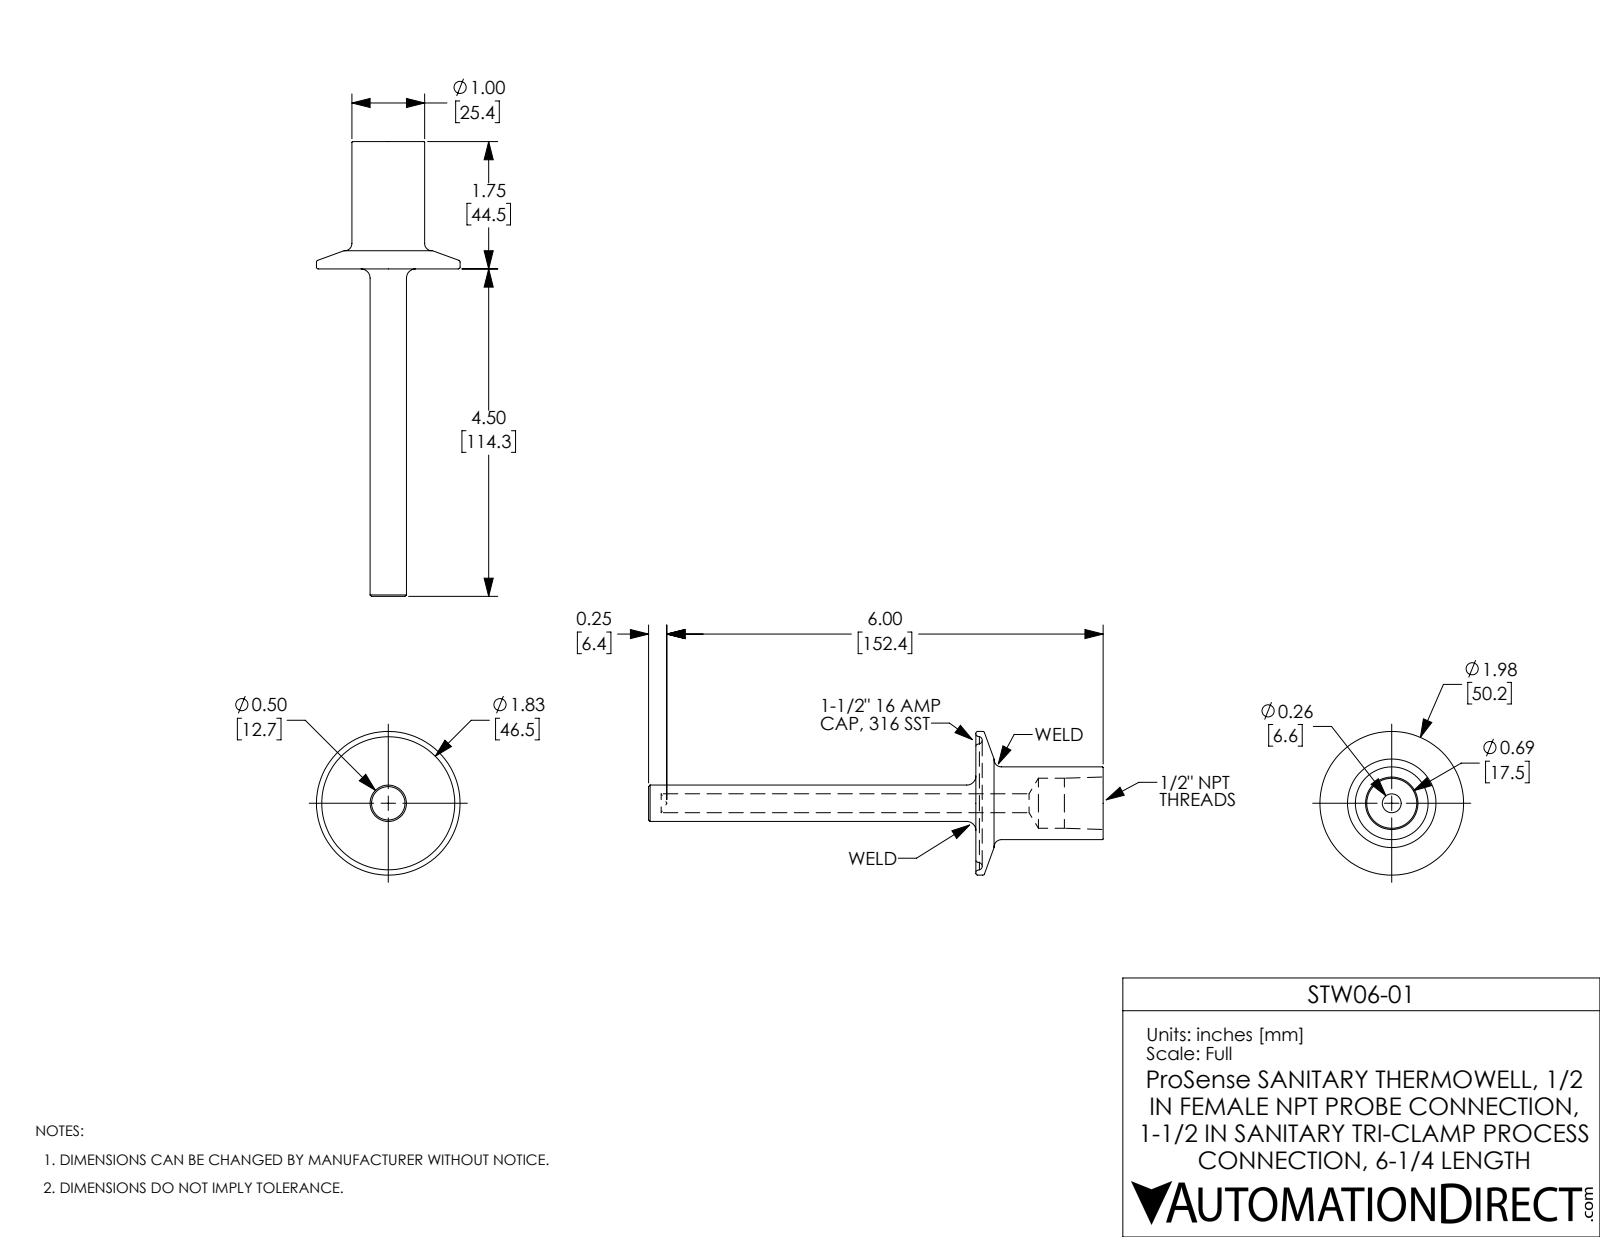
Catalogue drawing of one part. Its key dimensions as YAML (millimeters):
part_name: "STW06-01"
step_written_by: "SolidWorks 2017 (AUTOMOTIVE_DESIGN)"
units: millimeters
bodies: {solids: 1, faces: 45, planar: 5, cylindrical: 10, other: 30}
overall_size: [158.8, 50.2, 50.2]
volume: 33120
surface_area: 16150
round_holes:
  - {diameter: 6.6, count: 1}
  - {diameter: 17.5, count: 1}
round_bosses_or_shafts:
  - {diameter: 50.2, count: 1}
  - {diameter: 25.4, count: 1}
  - {diameter: 12.7, count: 1}
face_to_face_distances: [44.5, 158.8, 114.3, 38.1, 6.4, 120.7]
